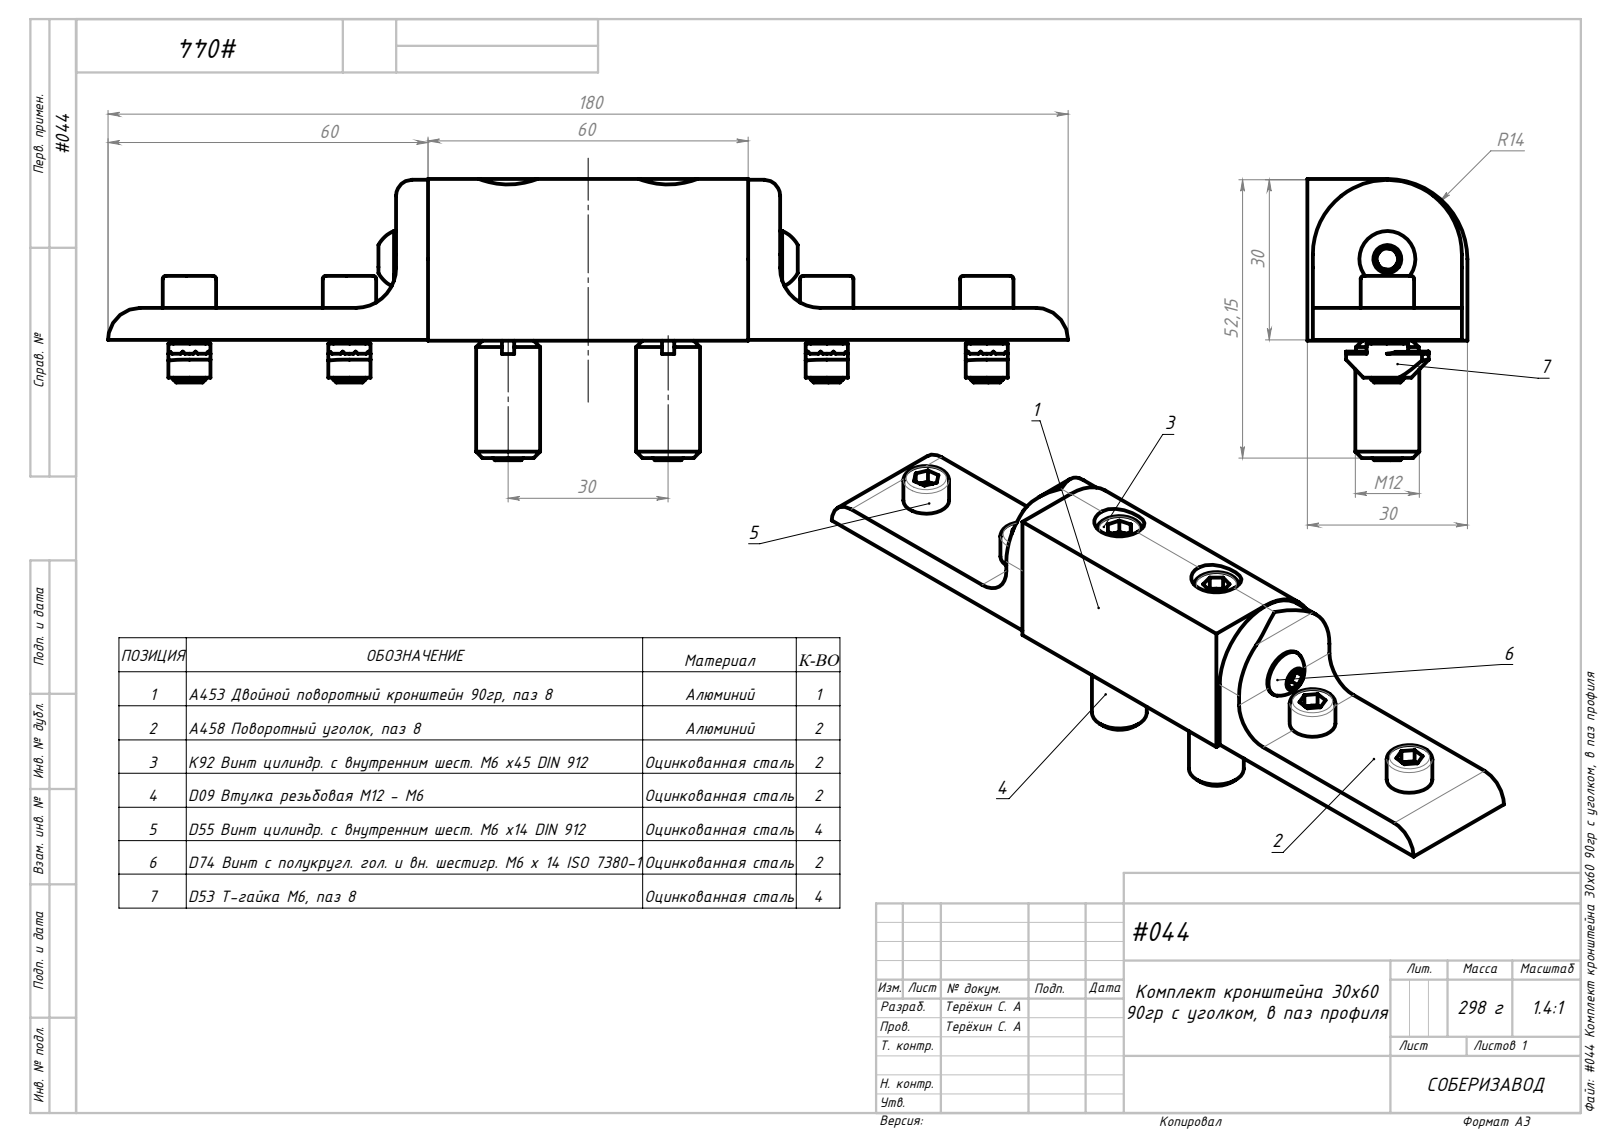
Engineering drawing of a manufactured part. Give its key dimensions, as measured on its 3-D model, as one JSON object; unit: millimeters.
{"part_name": "D53 Т-гайка М6, паз 8_00; D09 Втулка резьбовая М12 - М6 _00; D55 Винт цилиндр. с внутренним шест. М6 х14 DIN 912; D74 Винт с полукругл. гол. и вн. шестигр. М6 х 14 ISO 7380-1 (+4 more)", "step_written_by": "SolidWorks 2021 (AUTOMOTIVE_DESIGN)", "units": "millimeters", "bodies": {"solids": 17, "faces": 527, "planar": 286, "cylindrical": 99, "other": 142}, "overall_size": [180, 52.7, 30], "volume_mm3": 87111, "surface_area_mm2": 32793, "round_holes": [[6.3, 5], [5, 4], [5.5, 2], [6.15, 2], [11, 2], [5.15, 1]], "round_bosses_or_shafts": [[6, 7], [10, 6], [12, 2], [10.5, 1]], "partial_cylinders_radius": [[4, 8], [6.87, 8], [3, 2], [7.5, 2], [14, 2], [15, 1]], "face_to_face_distances": [6, 6.15, 60, 30, 1.02, 28.97, 27.95, 28.98, 1.03, 30.3], "hole_center_spacings": [59.75, 30, 29.75, 89.75, 119.5, 89.5, 149.5]}
